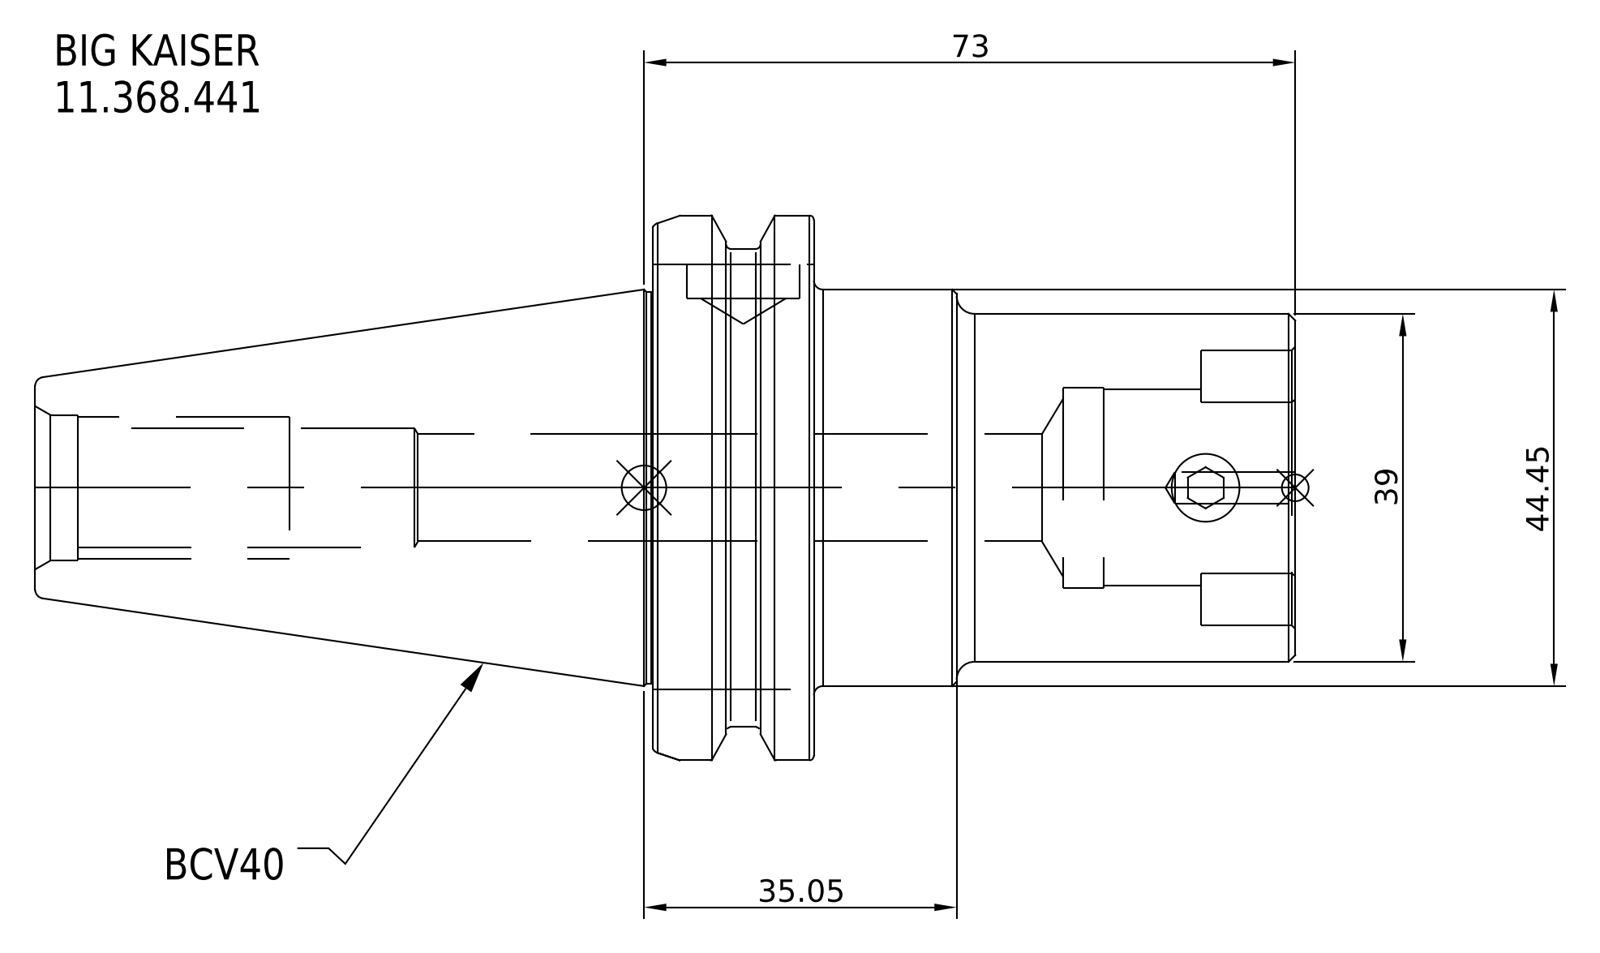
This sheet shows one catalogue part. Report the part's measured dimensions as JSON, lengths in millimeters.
{"part_name": "11.368.441", "step_written_by": "SolidWorks 2021 (CONFIG_CONTROL_DESIGN)", "units": "millimeters", "bodies": {"solids": 1, "faces": 16, "planar": 7, "cylindrical": 6, "other": 3}, "overall_size": [141.25, 63.5, 63.5], "volume_mm3": 187479, "surface_area_mm2": 24008, "round_bosses_or_shafts": [[63.5, 1], [56.36, 1], [44.45, 1], [39, 1]], "face_to_face_distances": [15.88, 53.95, 69.83, 141.25, 87.3, 71.42, 37.95, 16, 31.88, 103.3]}
